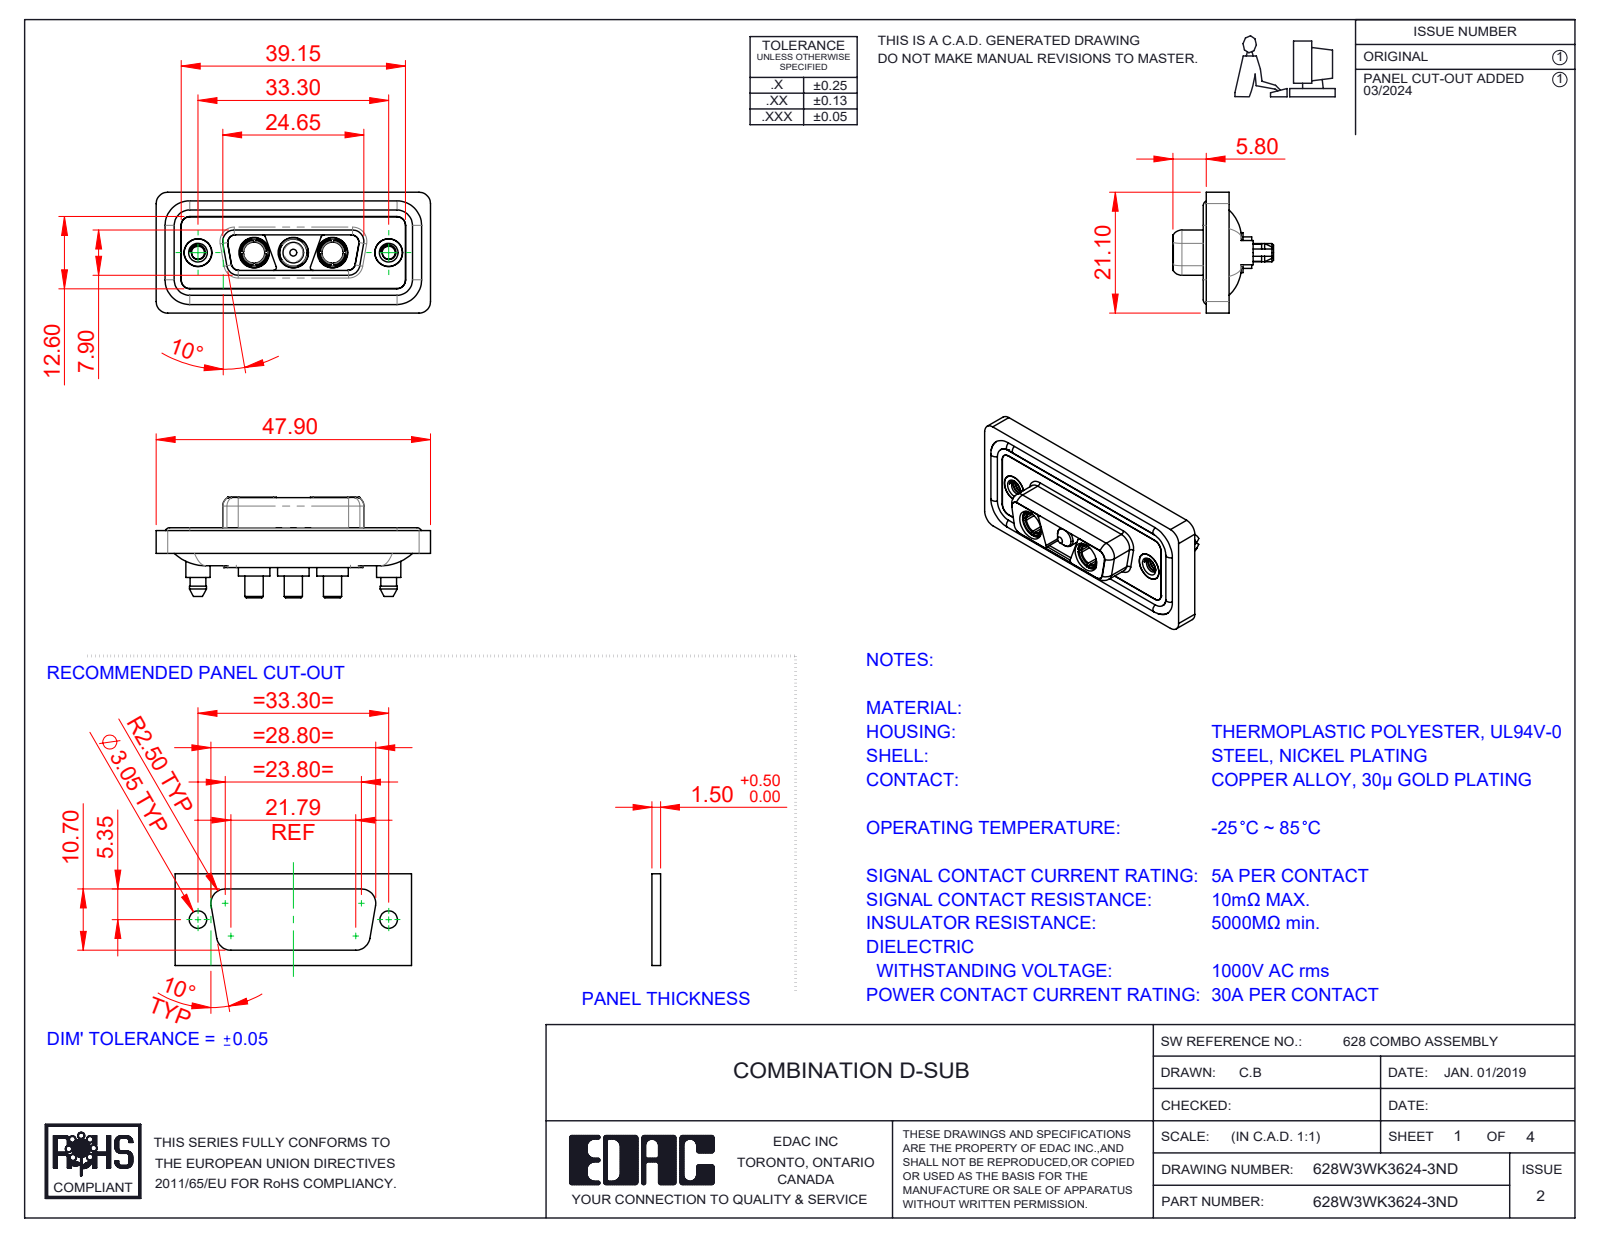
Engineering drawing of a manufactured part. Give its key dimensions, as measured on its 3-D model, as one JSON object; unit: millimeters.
{"part_name": "Power Socket_30A S; 628Combo Threaded Boardlock_D; 628Combo Waterproof Housing_15 Contacts; 628W3WK3624-3ND (+4 more)", "step_written_by": "SolidWorks 2023 (CONFIG_CONTROL_DESIGN)", "units": "millimeters", "bodies": {"solids": 13, "faces": 649, "planar": 194, "cylindrical": 306, "other": 149}, "overall_size": [47.9, 21.1, 17.55], "volume_mm3": 6035, "surface_area_mm2": 9858, "round_holes": [[4.85, 5], [5.3, 3], [2.26, 2], [3.7, 2], [4, 2], [4.05, 2], [5, 2]], "round_bosses_or_shafts": [[1.6, 4], [5.5, 3], [5.2, 3], [4.75, 3], [3.75, 3], [3.2, 3], [5.4, 2], [4.96, 2]], "partial_cylinders_radius": [[1.5, 24], [2, 20], [1.35, 12], [1.6, 10], [0.5, 8], [0.25, 4], [0.6, 4], [0.65, 4]], "face_to_face_distances": [0.4, 1.6, 1.8, 0.5, 1.1, 2.9, 5.65, 7.05, 1.5, 5.35], "hole_center_spacings": [6.85, 9.8, 16.65, 23.5, 13.7, 33.3]}
